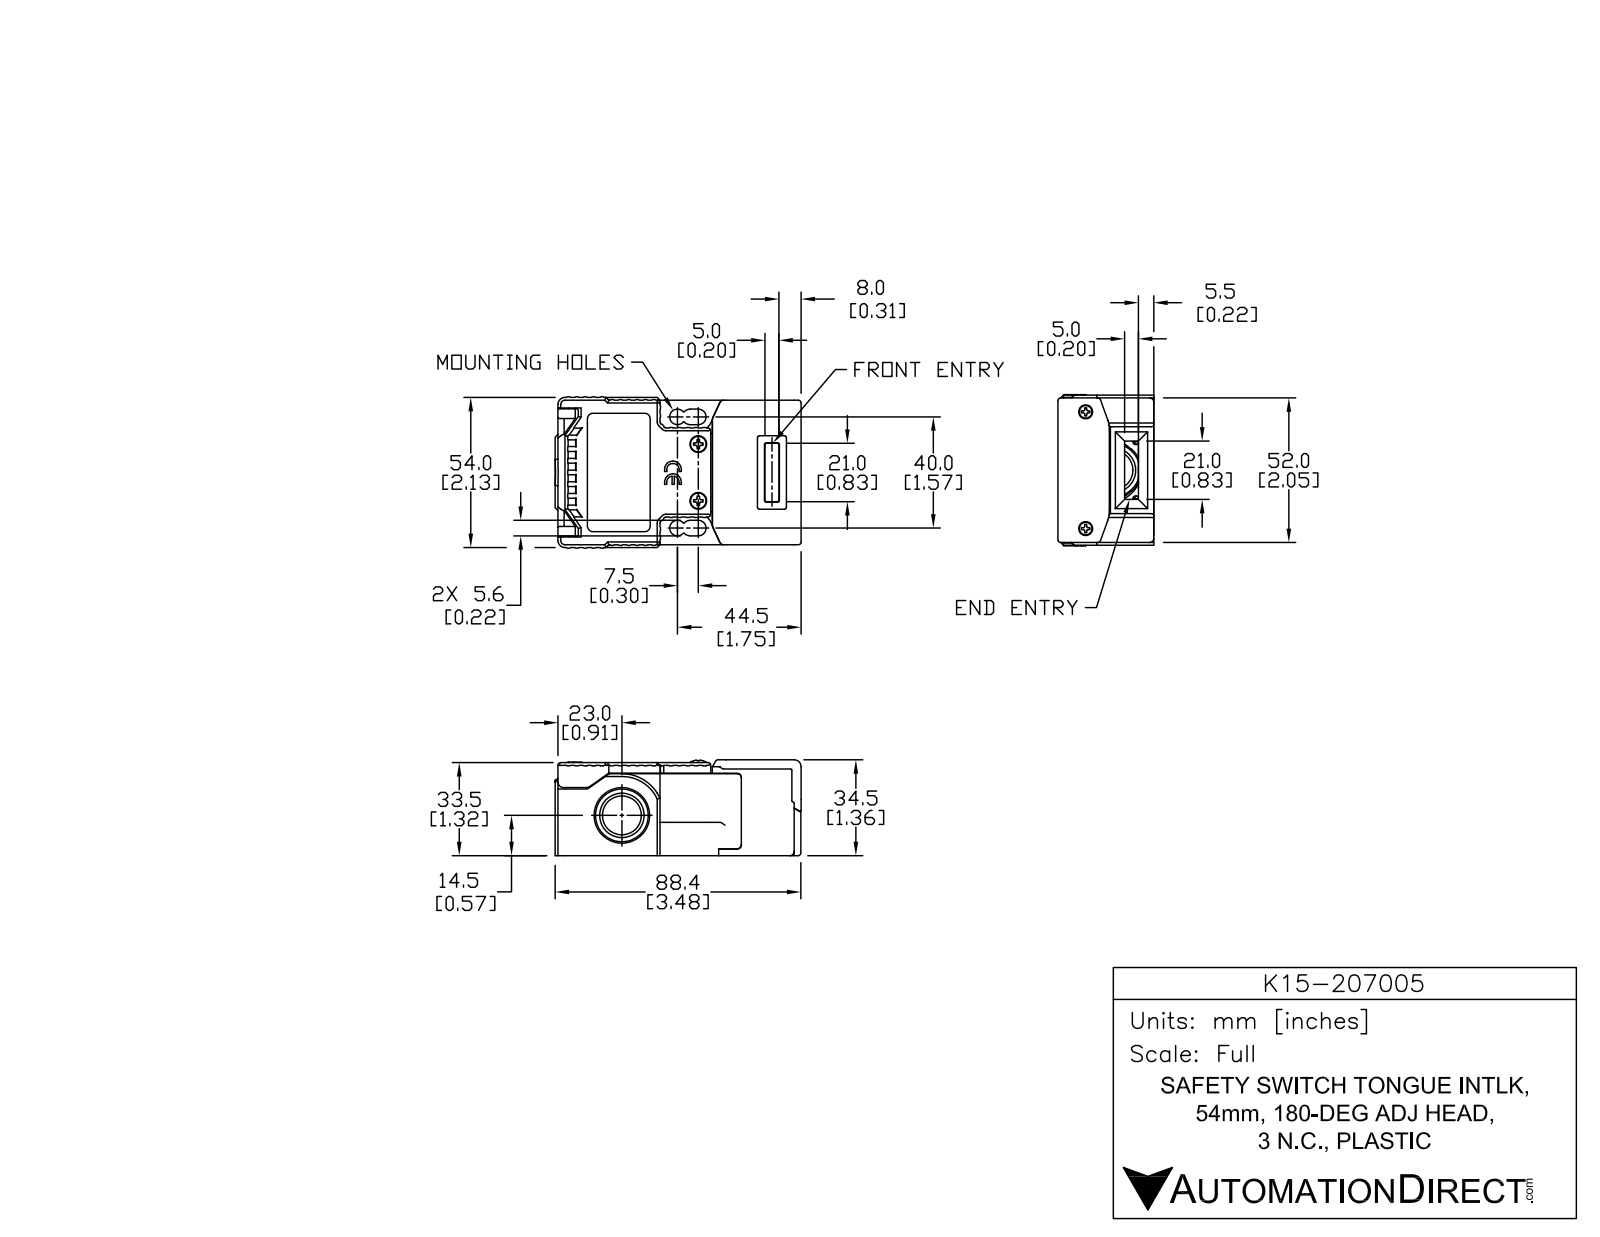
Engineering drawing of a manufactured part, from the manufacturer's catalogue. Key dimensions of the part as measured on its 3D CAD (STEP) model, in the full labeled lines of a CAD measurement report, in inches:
Part name (STEP PRODUCT): K-15-207005
STEP written by: SolidWorks 2013 (AUTOMOTIVE_DESIGN)
Units: inches
Bodies: 1 solid, 376 faces (166 planar, 137 cylindrical, 73 other)
Overall size (bounding box): 3.524 × 2.283 × 1.362
Volume: 8.748 in³ · Surface area: 35.93 in²
Round holes (diameter × count): ⌀0.761 ×1, ⌀0.787 ×1
Round bosses / shafts (diameter × count): ⌀0.177 ×2
Partial cylindrical surfaces — rounded edges, fillets, slot ends (radius × count): R0.02 ×94, R0.11 ×6, R0.118 ×4, R0.157 ×3
Main face-to-face distances: 0.118, 2.165, 1.319, 0.039, 2.047, 1.358, 1.317, 0.041, 3.441, 0.504
